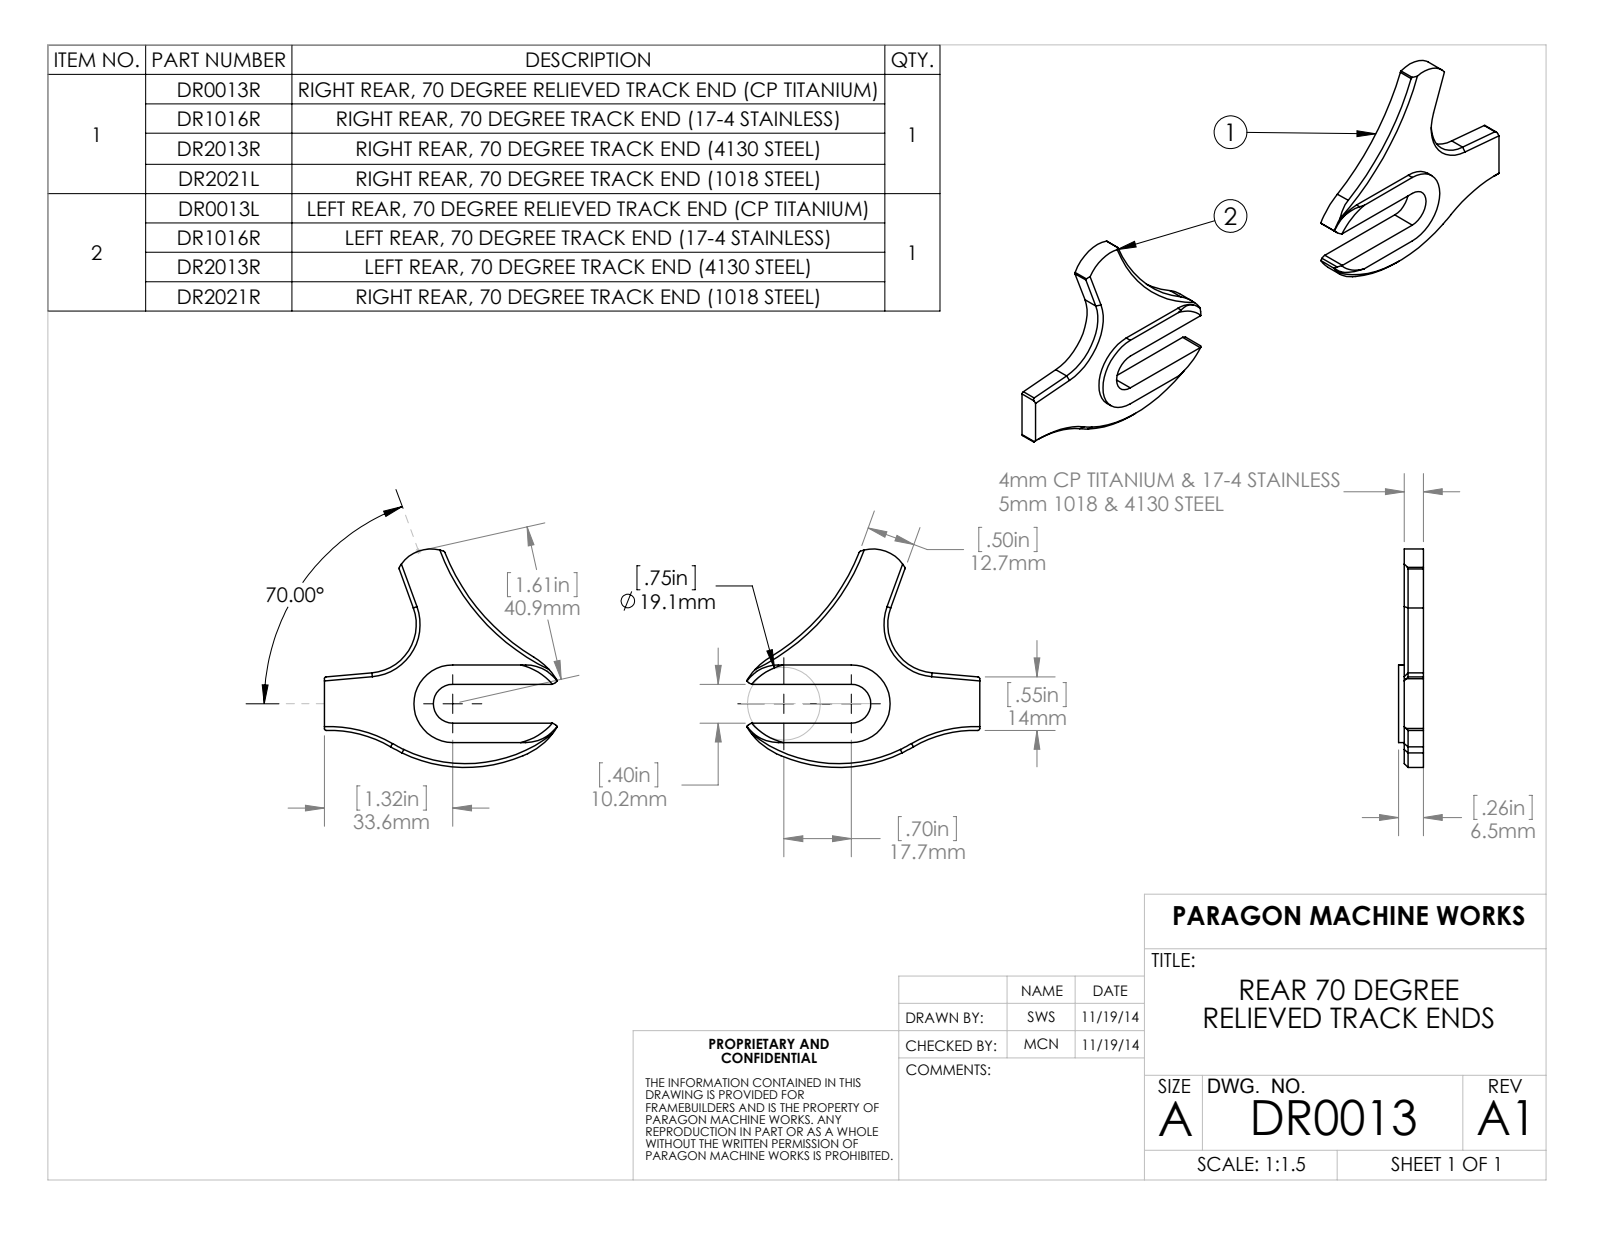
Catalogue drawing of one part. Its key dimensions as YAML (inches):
part_name: "DR0013LR; DR0013L; DR0013R"
step_written_by: "SolidWorks 2012 (AUTOMOTIVE_DESIGN)"
units: inches
bodies: {solids: 2, faces: 80, planar: 28, cylindrical: 38, other: 14}
overall_size: [6.759, 2.253, 0.256]
volume: 1.037
surface_area: 14.36
partial_cylinders:
  - {radius: 0.02, count: 8}
  - {radius: 0.06, count: 4}
  - {radius: 0.4, count: 4}
  - {radius: 0.698, count: 4}
  - {radius: 1.8, count: 4}
  - {radius: 0.2, count: 2}
  - {radius: 0.375, count: 2}
  - {radius: 0.5, count: 2}
face_to_face_distances: [0.197, 0.256, 0.059, 0.4, 0.2, 0.6, 6.758, 0.8, 1.714]
